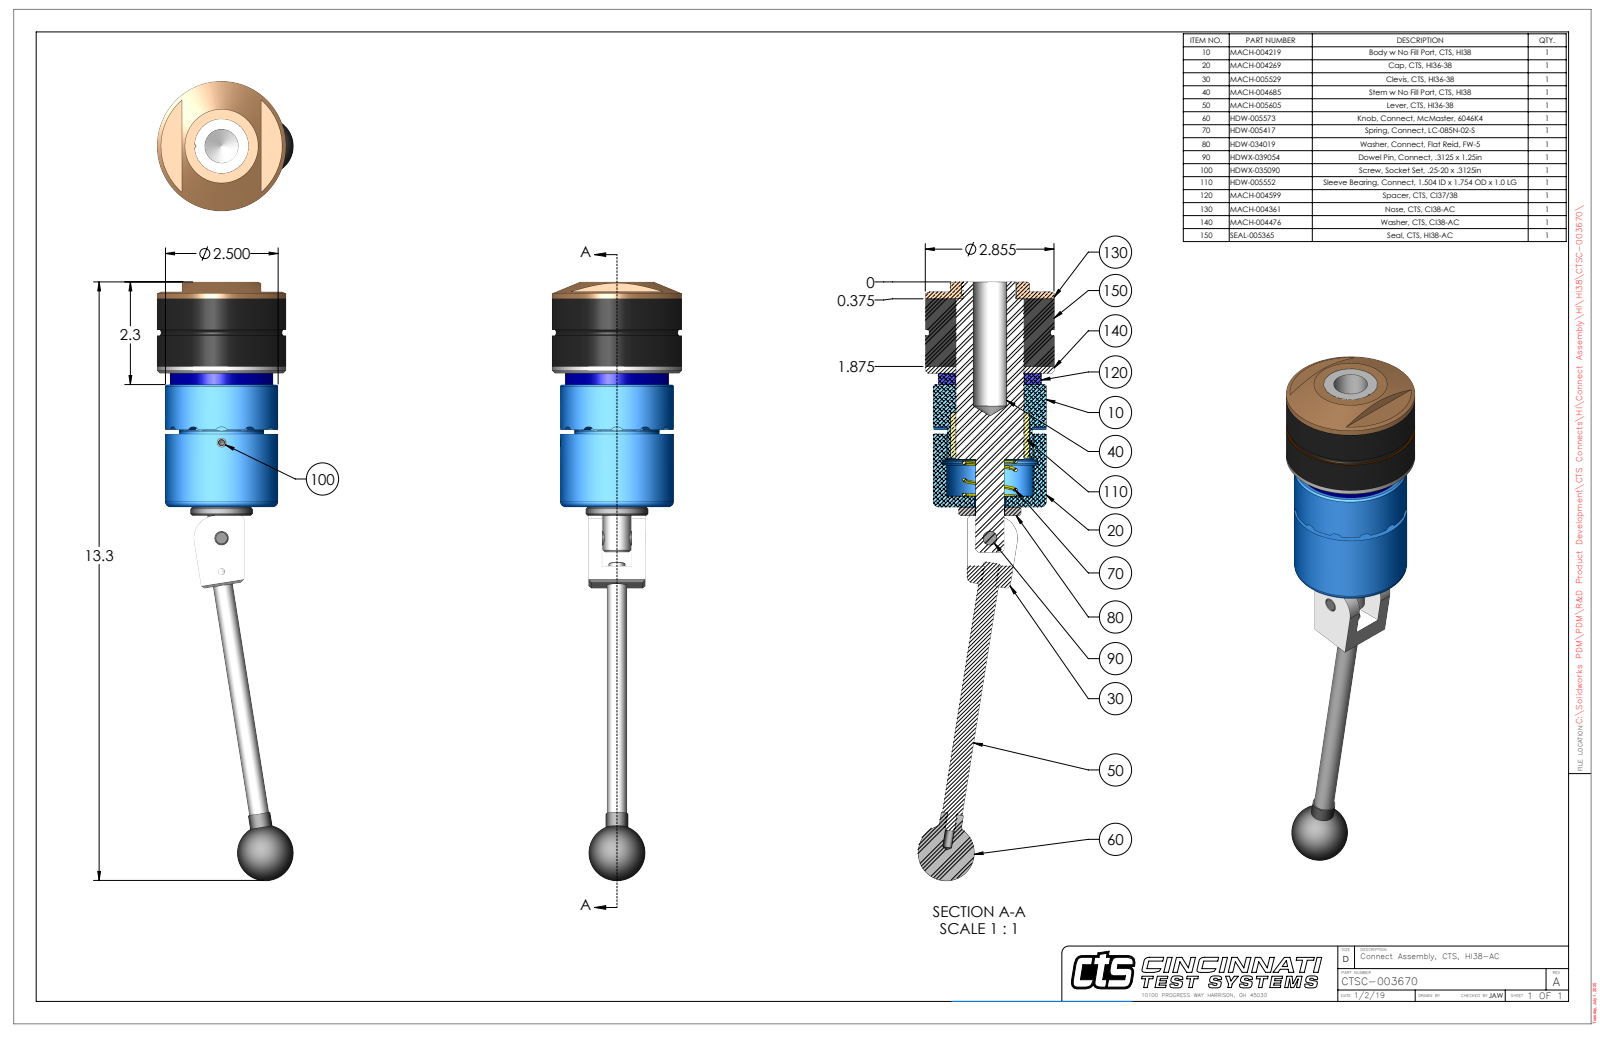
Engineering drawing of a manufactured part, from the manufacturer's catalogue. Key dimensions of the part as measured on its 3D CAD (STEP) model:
Part name (STEP PRODUCT): CTSC-003670
STEP written by: SolidWorks 2023 (AUTOMOTIVE_DESIGN)
Units: inches
Bodies: 10 solids, 275 faces (98 planar, 108 cylindrical, 69 other)
Overall size (bounding box): 13.275 × 3.02 × 2.855
Volume: 28.61 in³ · Surface area: 150.3 in²
Round holes (diameter × count): ⌀0.201 ×2, ⌀0.15 ×1, ⌀0.311 ×1, ⌀0.313 ×1, ⌀0.314 ×1, ⌀0.656 ×1, ⌀0.696 ×1, ⌀0.75 ×1, ⌀1.172 ×1, ⌀1.495 ×1, ⌀1.501 ×1, ⌀1.51 ×1
Round bosses / shafts (diameter × count): ⌀2.855 ×1, ⌀2.855 ×1, ⌀2.5 ×1, ⌀2.281 ×1, ⌀1.875 ×1, ⌀1.5 ×1, ⌀1.496 ×1, ⌀1.38 ×1
Partial cylindrical surfaces — rounded edges, fillets, slot ends (radius × count): R0.12 ×12, R0.029 ×2, R0.5 ×1, R1.209 ×1
Main face-to-face distances: 1.5, 0.152, 1.652, 0.25, 0.402, 1.902, 2.713, 2.963, 3.115, 4.615
Hole centre spacings: 0.74, 2.118, 2.858
